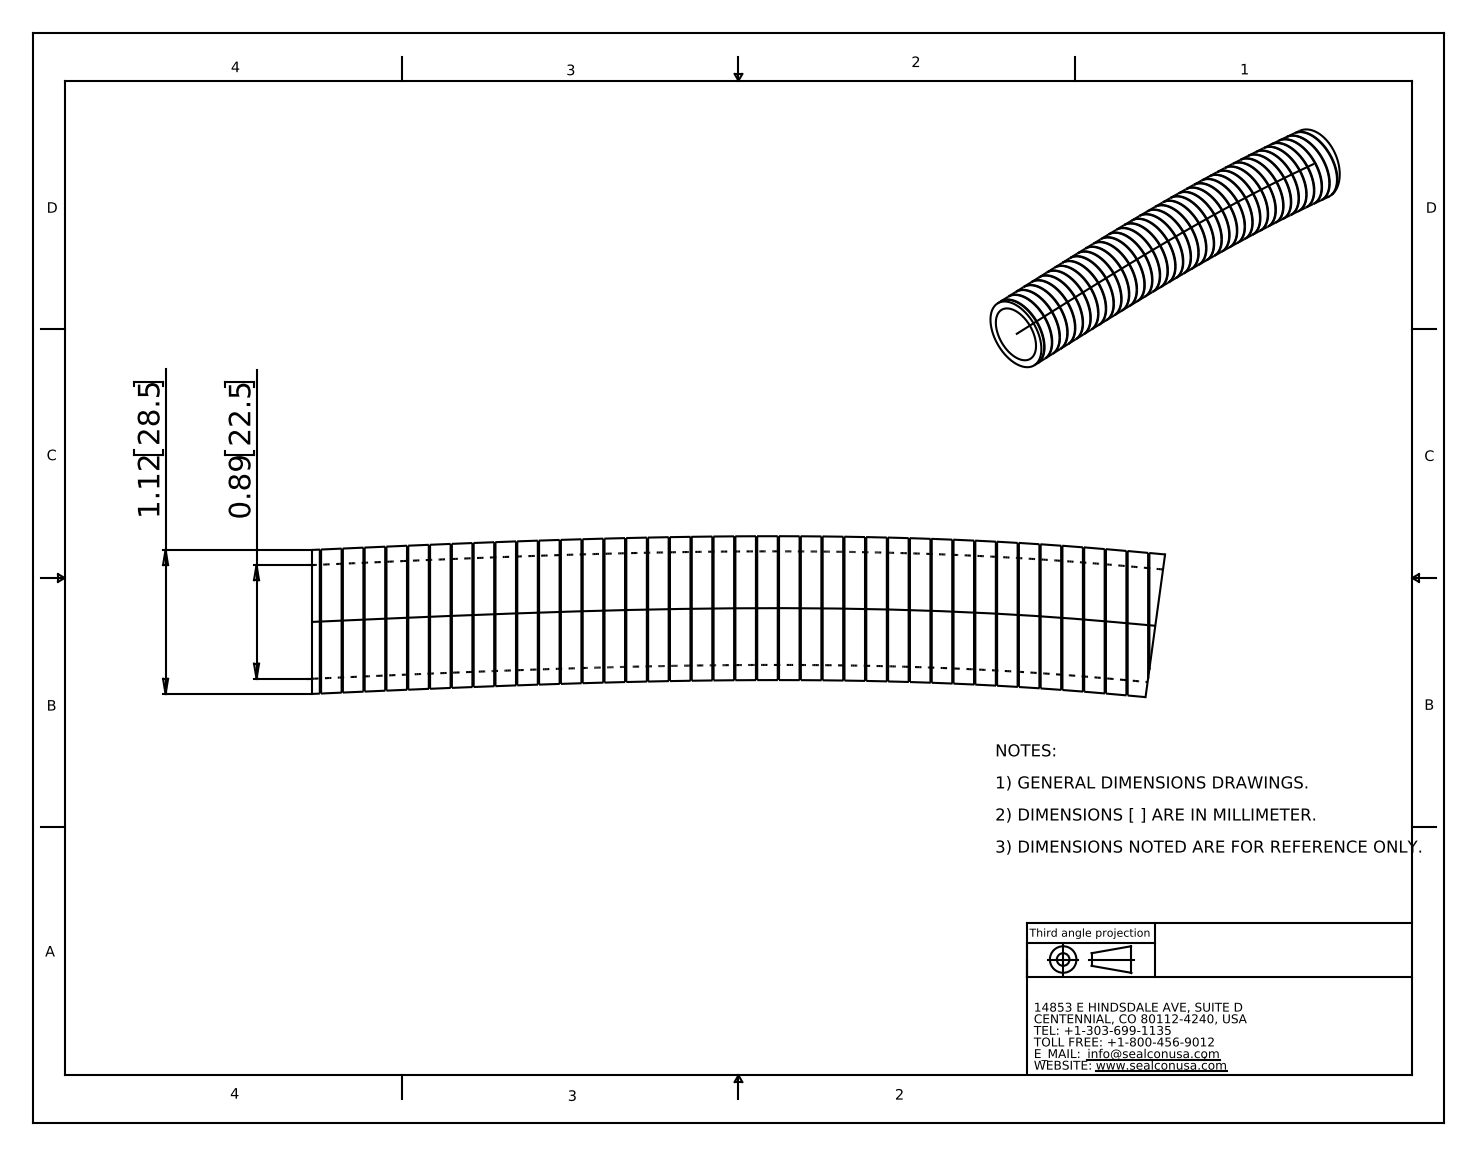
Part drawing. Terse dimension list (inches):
name: SM-1013-HY
written by: SolidWorks 2007 (AUTOMOTIVE_DESIGN)
unit: in
bodies: 1 solid, 240 faces (80 planar, 77 cylindrical, 83 other)
size: 6.646 × 1.252 × 1.12
volume: 2.272 in³; area: 64.57 in²
bosses: 37× ⌀0.94
face distances: 0.17, 0.339, 0.169, 0.18, 0.34, 0.509, 0.159, 0.508, 0.519, 0.509
